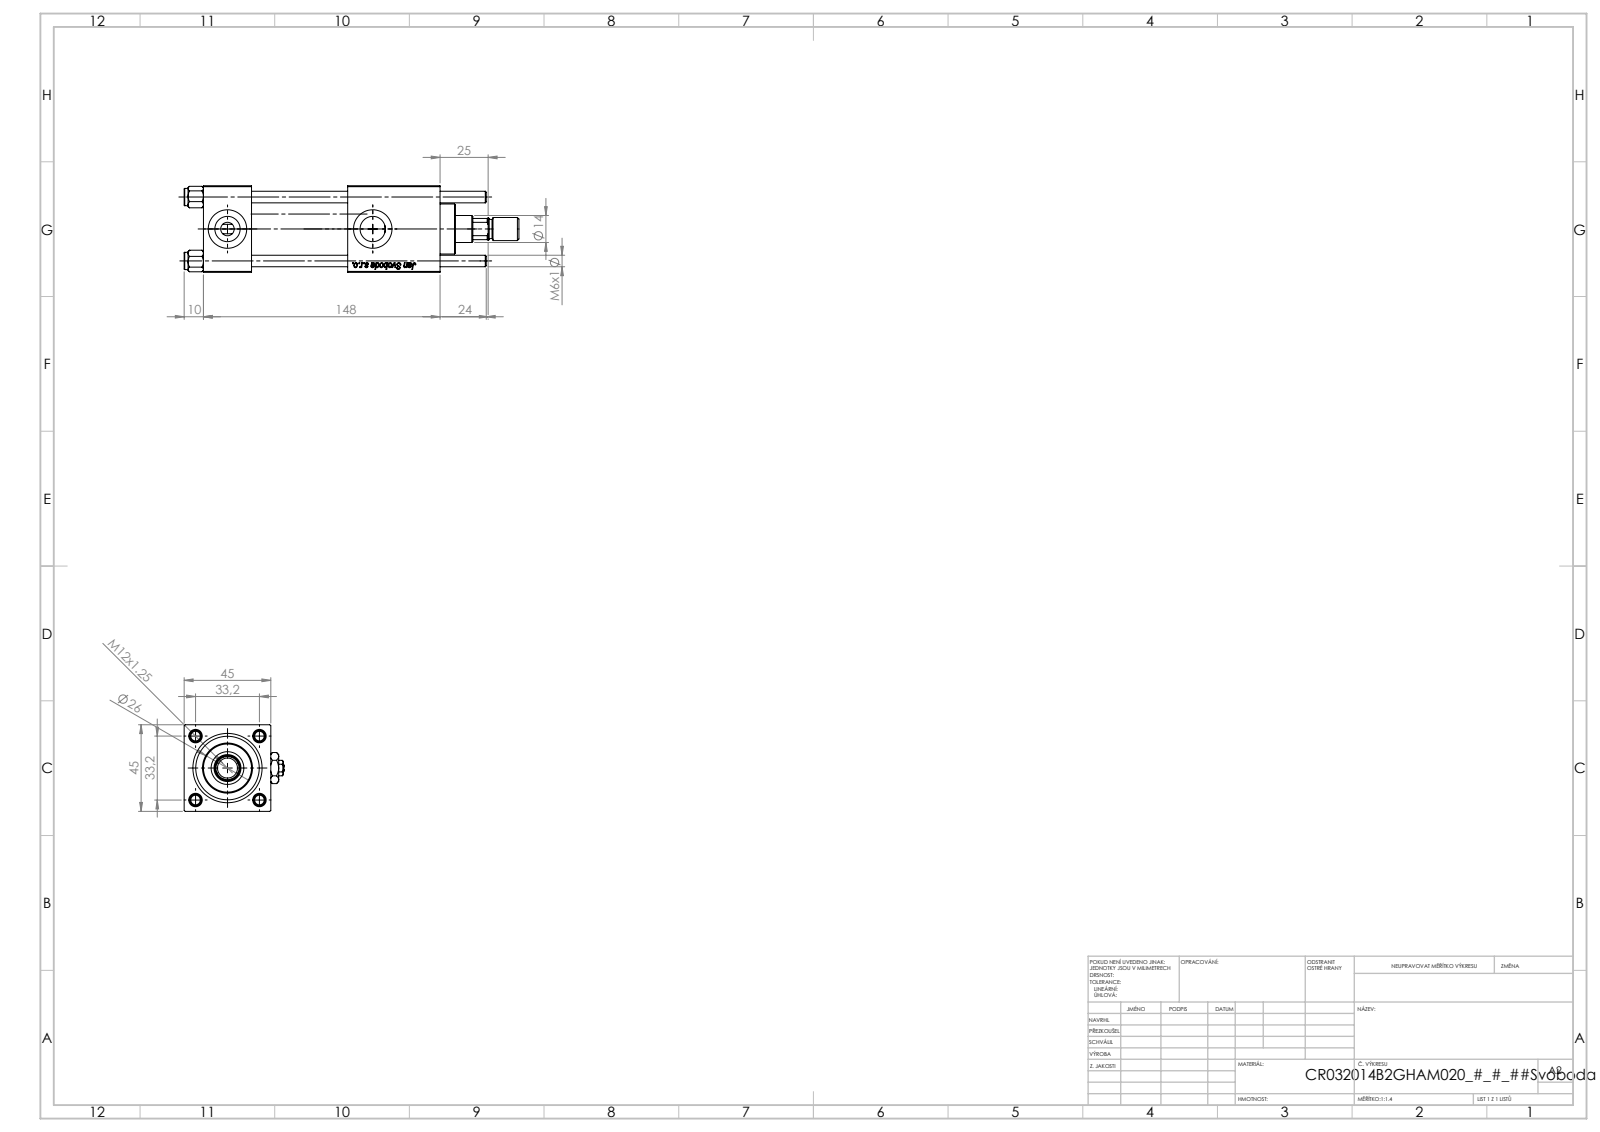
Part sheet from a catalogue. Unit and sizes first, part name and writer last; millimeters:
Units: millimetres
Overall size (bounding box): 174 × 52 × 45
Round holes (diameter × count): ⌀6 ×4, ⌀7 ×2, ⌀13.16 ×2, ⌀20 ×2, ⌀6.5 ×1, ⌀14 ×1, ⌀17 ×1, ⌀24 ×1, ⌀32 ×1, ⌀33 ×1
Round bosses / shafts (diameter × count): ⌀9 ×4, ⌀38 ×1, ⌀26 ×1, ⌀12 ×1, ⌀10 ×1
Partial cylindrical surfaces — rounded edges, fillets, slot ends (radius × count): R6.5 ×1
Main face-to-face distances: 45, 25, 123, 98, 50, 75, 48, 94.3, 69.3, 19.3
Hole centre spacings: 23.48, 33.2, 46.95, 75.5
Volume: 199 248 mm³ · Surface area: 74 500 mm²
Bodies: 13 solids, 1222 faces (458 planar, 88 cylindrical, 676 other)
Part name (STEP PRODUCT): NUT_M5_B; V215CR_B_TYCINKA; V215CR_VCP_B; Zatka_pro_OIL_PORT (+3 more)
STEP written by: SolidWorks 2019 (CONFIG_CONTROL_DESIGN)
